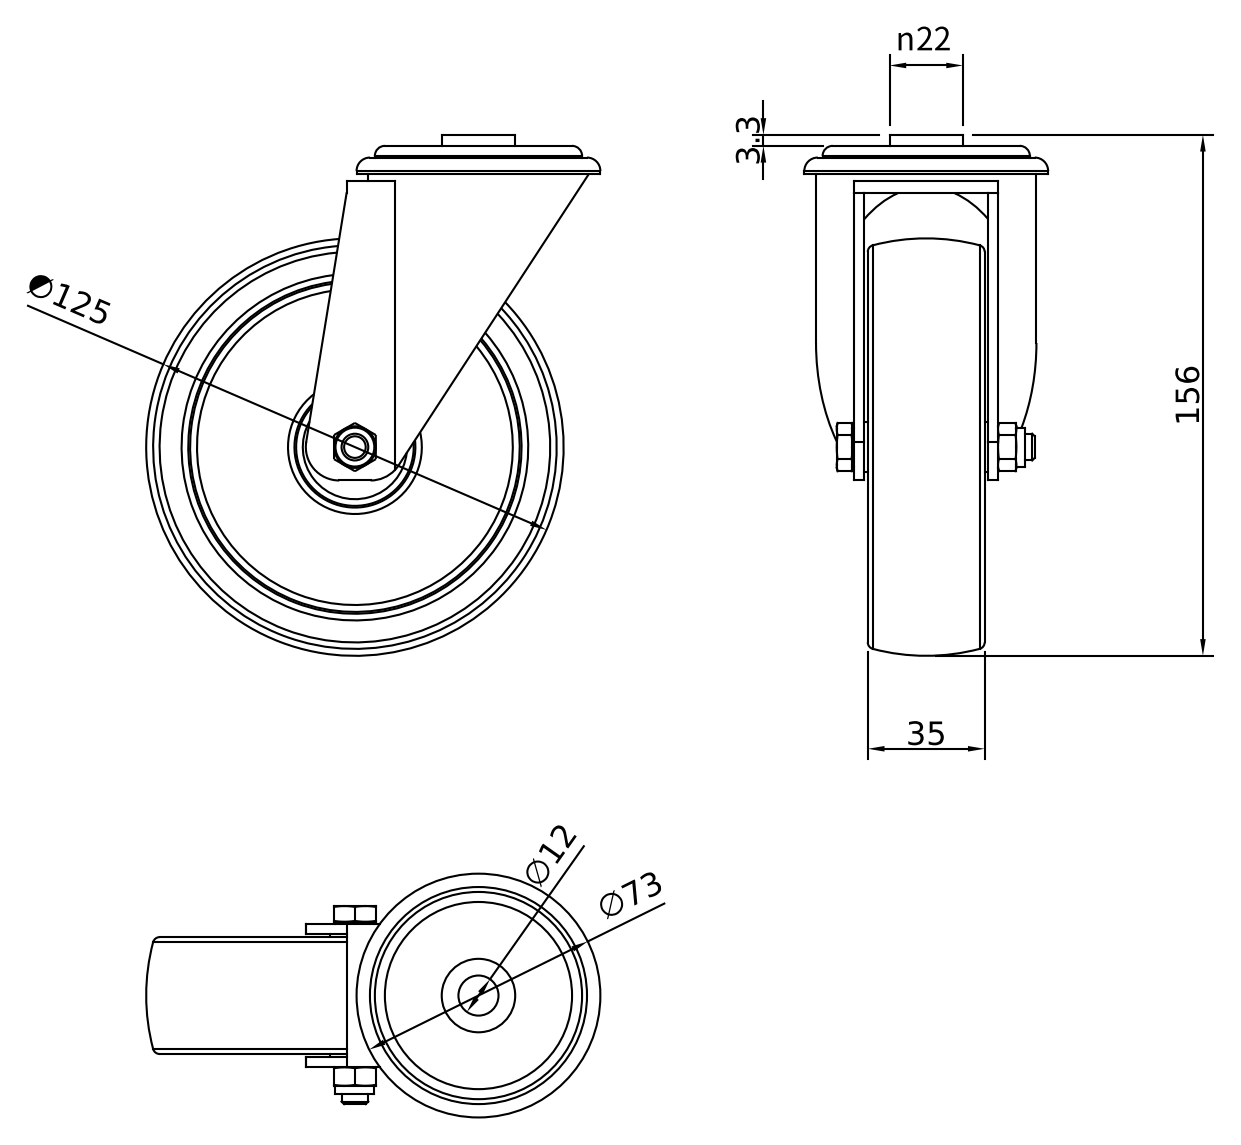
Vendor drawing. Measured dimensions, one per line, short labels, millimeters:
name: CRUST0000186; 440000025955; 440000025954; 440000025953
written by: Autodesk Inventor 2022 (AUTOMOTIVE_DESIGN)
unit: mm
bodies: 3 solids, 106 faces (42 planar, 20 cylindrical, 44 other)
size: 156 × 136 × 73
volume: 295 762 mm³; area: 81 691 mm²
holes: 1× ⌀9, 1× ⌀12, 1× ⌀15, 1× ⌀61
bosses: 1× ⌀73, 1× ⌀66, 1× ⌀62.05, 1× ⌀22, 1× ⌀11.63, 1× ⌀8
rounds: 2× R10
face distances: 1, 36, 3, 4, 39, 40, 35, 10.7, 37, 43
